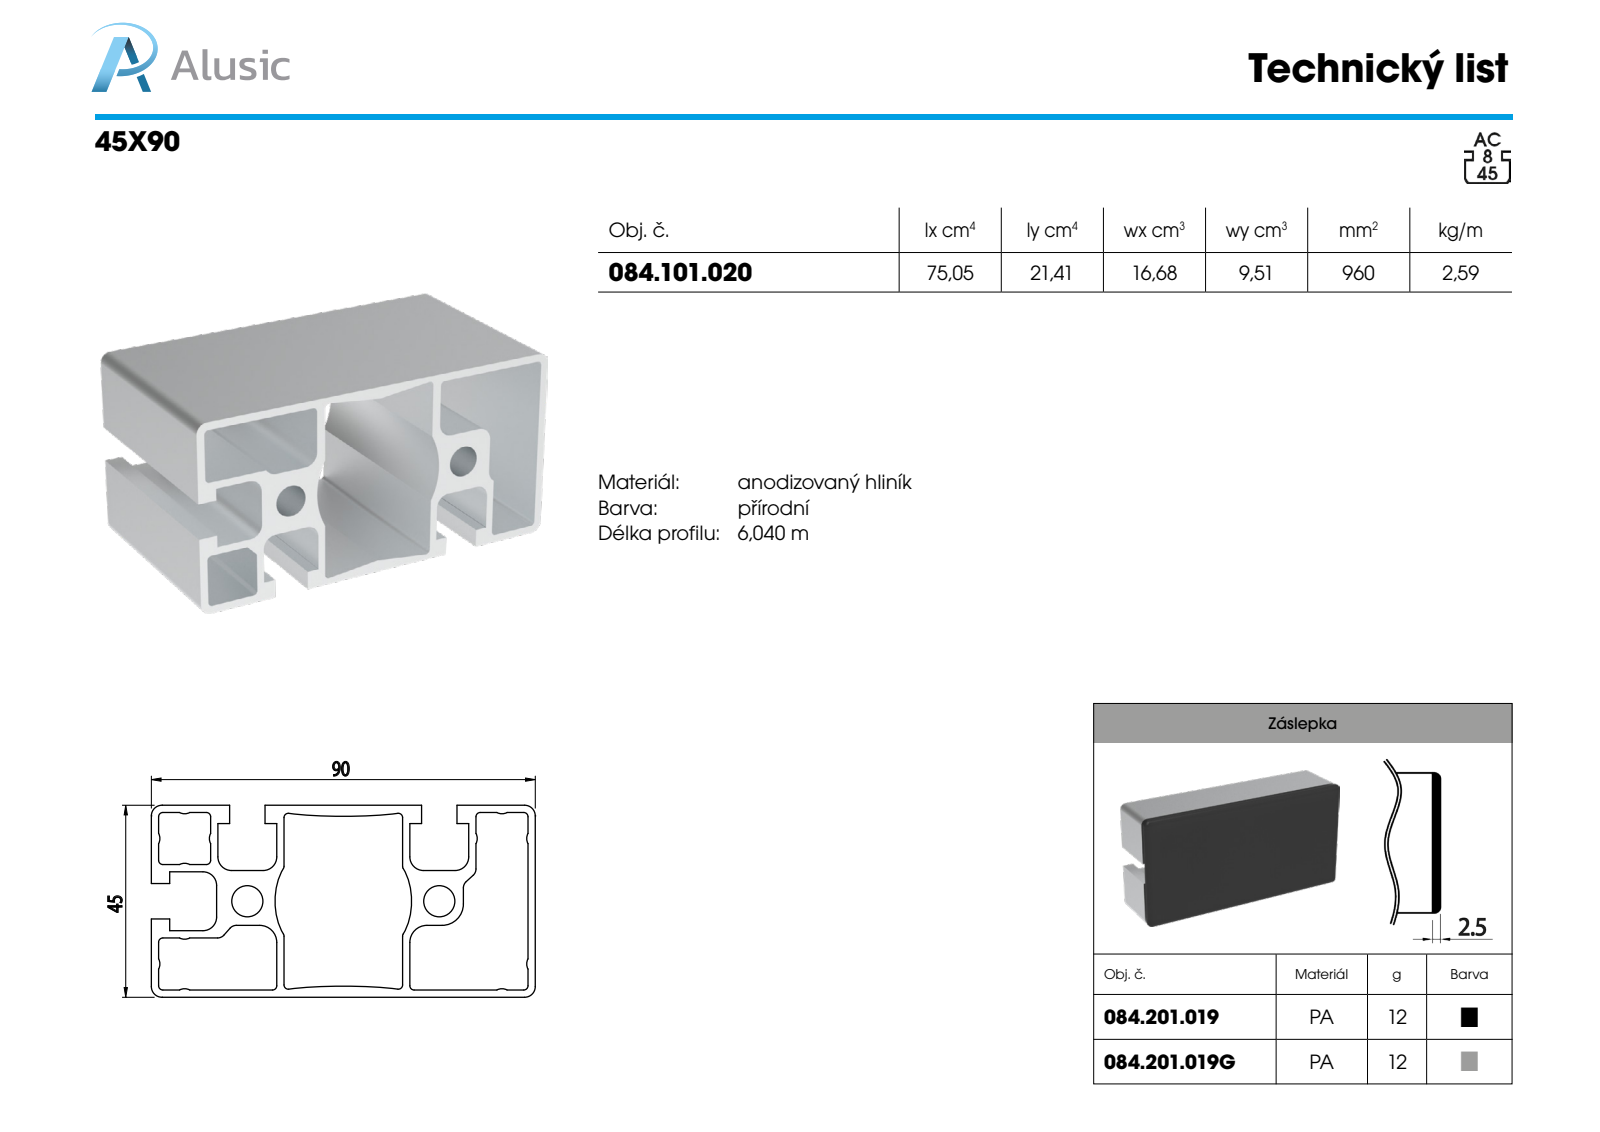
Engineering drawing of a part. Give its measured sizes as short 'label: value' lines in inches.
name: 084.101.020
written by: SolidWorks 2018 (AUTOMOTIVE_DESIGN)
unit: in
bodies: 1 solid, 91 faces (55 planar, 36 cylindrical, 0 other)
size: 3.937 × 3.543 × 1.772
volume: 6.213 in³; area: 131 in²
holes: 2× ⌀0.287
rounds: 14× R0.039, 7× R0.118, 4× R0.098, 4× R0.126, 2× R0.654
face distances: 0.071, 1.772, 0.543, 1.224, 1.701, 1.154, 0.531, 3.472, 2.319, 0.067
hole spacings: 1.772
